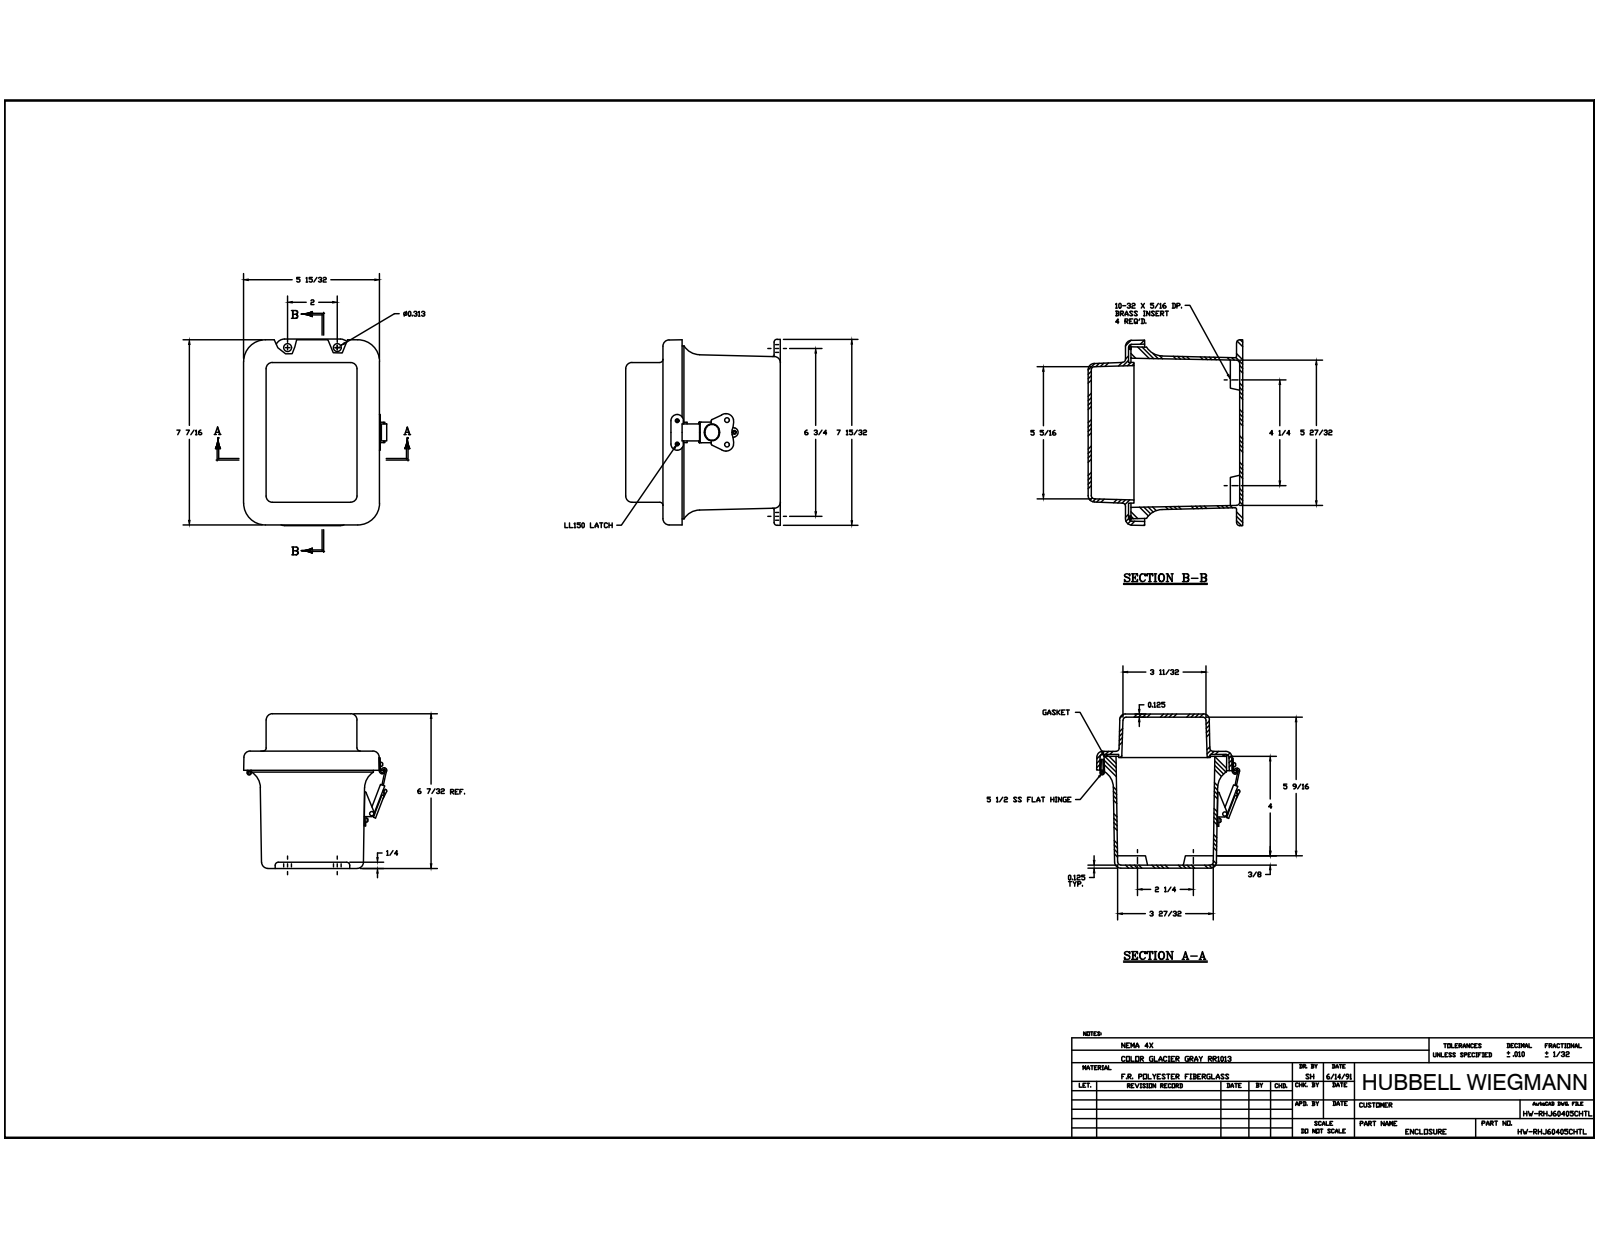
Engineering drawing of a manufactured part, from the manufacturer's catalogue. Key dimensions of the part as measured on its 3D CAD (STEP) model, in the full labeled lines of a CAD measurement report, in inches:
Part name (STEP PRODUCT): J604HL_5; RMINS45821P_59; RMINS45821P_60; RMINS45821P_61 (+8 more)
STEP written by: Autodesk Inventor 2014 (AUTOMOTIVE_DESIGN)
Units: inches
Bodies: 30 solids, 777 faces (317 planar, 290 cylindrical, 170 other)
Overall size (bounding box): 7.474 × 6.227 × 5.674
Volume: 33.66 in³ · Surface area: 459.5 in²
Round holes (diameter × count): ⌀0.14 ×9, ⌀0.131 ×5, ⌀0.152 ×5, ⌀0.156 ×4, ⌀0.218 ×4, ⌀0.13 ×2, ⌀0.165 ×2, ⌀0.197 ×2, ⌀0.085 ×1, ⌀0.106 ×1, ⌀0.118 ×1, ⌀0.138 ×1
Round bosses / shafts (diameter × count): ⌀0.25 ×9, ⌀0.125 ×9, ⌀0.27 ×4, ⌀0.583 ×1, ⌀0.524 ×1, ⌀0.209 ×1, ⌀0.185 ×1, ⌀0.155 ×1
Partial cylindrical surfaces — rounded edges, fillets, slot ends (radius × count): R0.031 ×20, R0.125 ×20, R0.25 ×12, R0.079 ×10, R0.037 ×4, R0.039 ×4, R0.045 ×4, R0.047 ×4
Main face-to-face distances: 0.125, 4.602, 6.102, 1.5, 6.227, 1.625, 4.477, 5.977, 0.774, 4.727
Hole centre spacings: 2.5, 3.339, 0.276, 0.469, 0.5, 0.826, 0.826, 0.938
